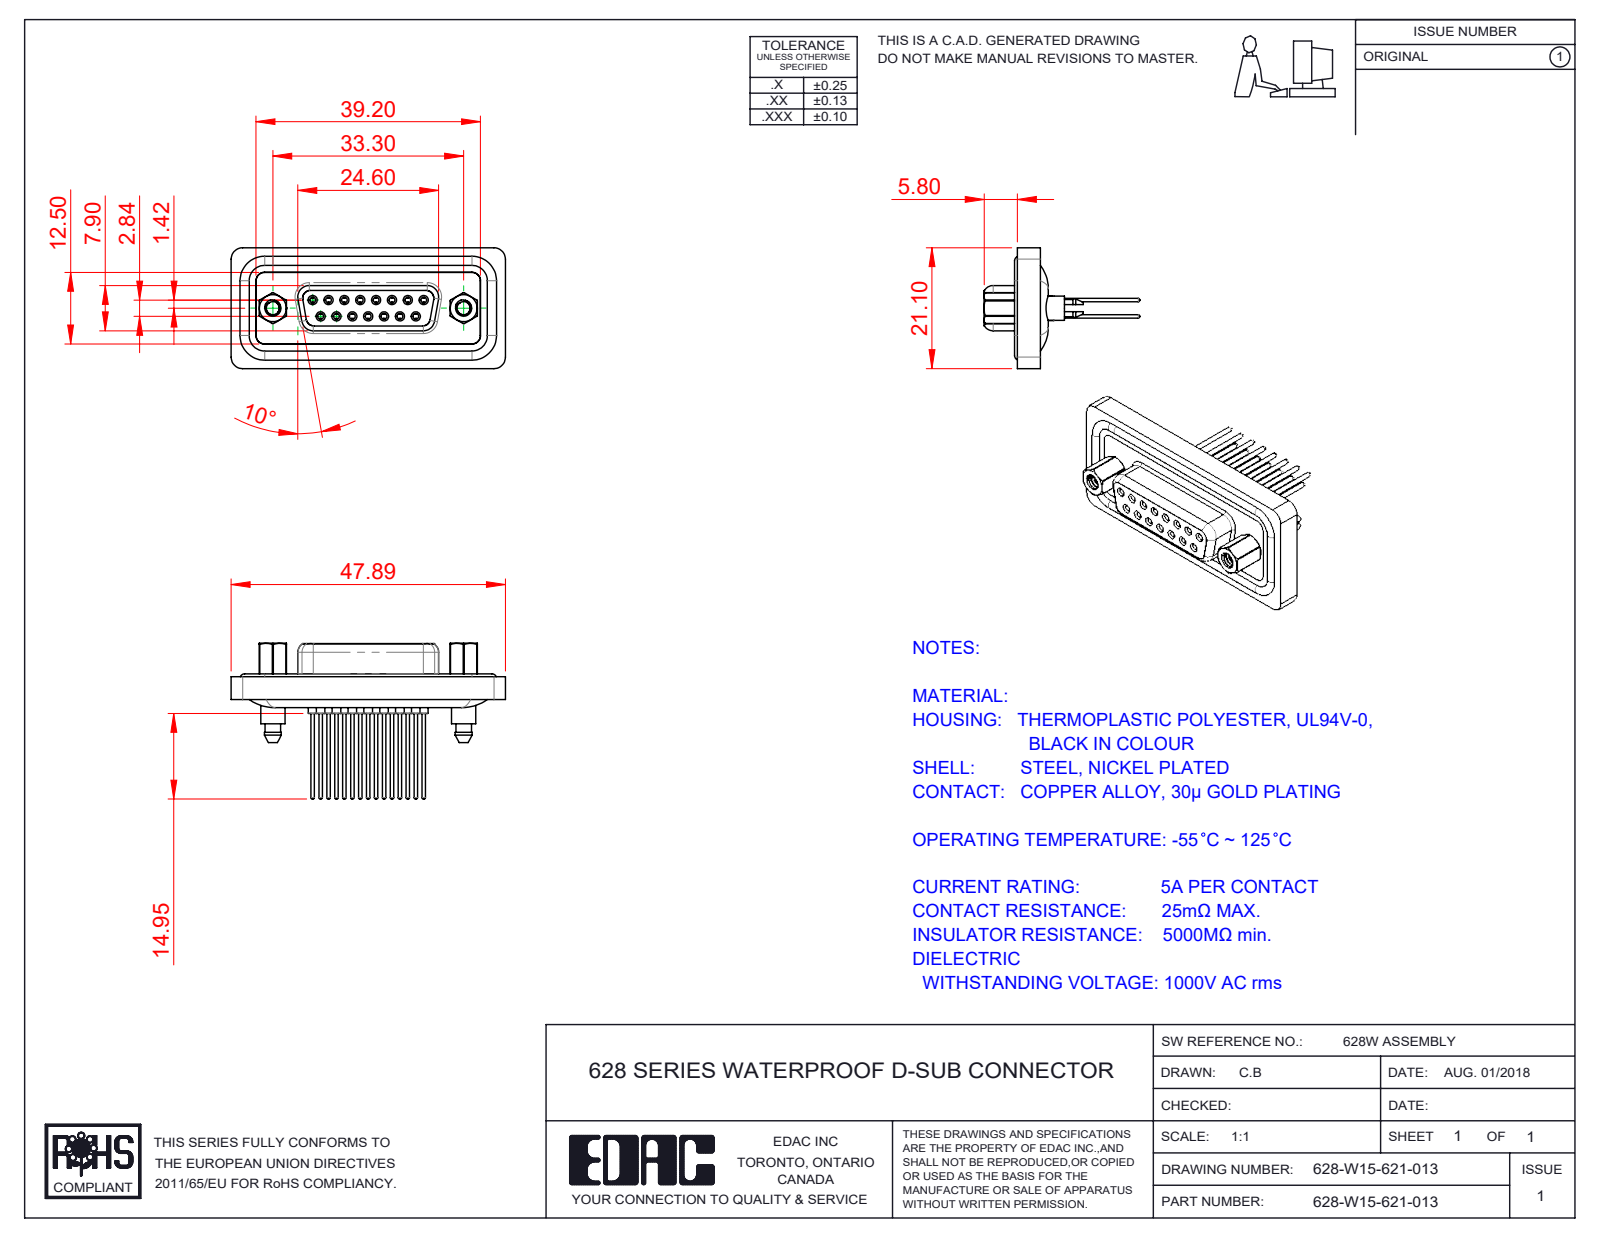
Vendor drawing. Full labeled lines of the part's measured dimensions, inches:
Part name (STEP PRODUCT): 628W Housing_15 Contacts; 628W Shell Front_15 Contacts; 628-W15-621-013; 628W Contact Row 2_21 (+4 more)
STEP written by: SolidWorks 2020 (CONFIG_CONTROL_DESIGN)
Units: inches
Bodies: 23 solids, 1324 faces (340 planar, 563 cylindrical, 421 other)
Overall size (bounding box): 1.885 × 1.071 × 0.831
Volume: 0.345 in³ · Surface area: 15.44 in²
Round holes (diameter × count): ⌀0.039 ×15, ⌀0.043 ×15, ⌀0.059 ×15, ⌀0.067 ×15, ⌀0.071 ×15, ⌀0.079 ×15, ⌀0.089 ×2, ⌀0.09 ×2, ⌀0.157 ×2, ⌀0.167 ×2, ⌀0.189 ×2
Round bosses / shafts (diameter × count): ⌀0.063 ×19, ⌀0.087 ×15, ⌀0.059 ×15, ⌀0.024 ×15, ⌀0.213 ×2, ⌀0.193 ×2, ⌀0.11 ×2, ⌀0.189 ×1
Partial cylindrical surfaces — rounded edges, fillets, slot ends (radius × count): R0.059 ×16, R0.079 ×16, R0.053 ×8, R0.063 ×6, R0.02 ×4, R0.035 ×4, R0.069 ×4, R0.106 ×4
Main face-to-face distances: 0.016, 0.071, 0.114, 0.098, 0.063, 0.043, 0.293, 0.537, 0.161, 0.177
Hole centre spacings: 0.124, 0.109, 0.218, 0.327, 0.125, 0.124, 0.436, 0.198
